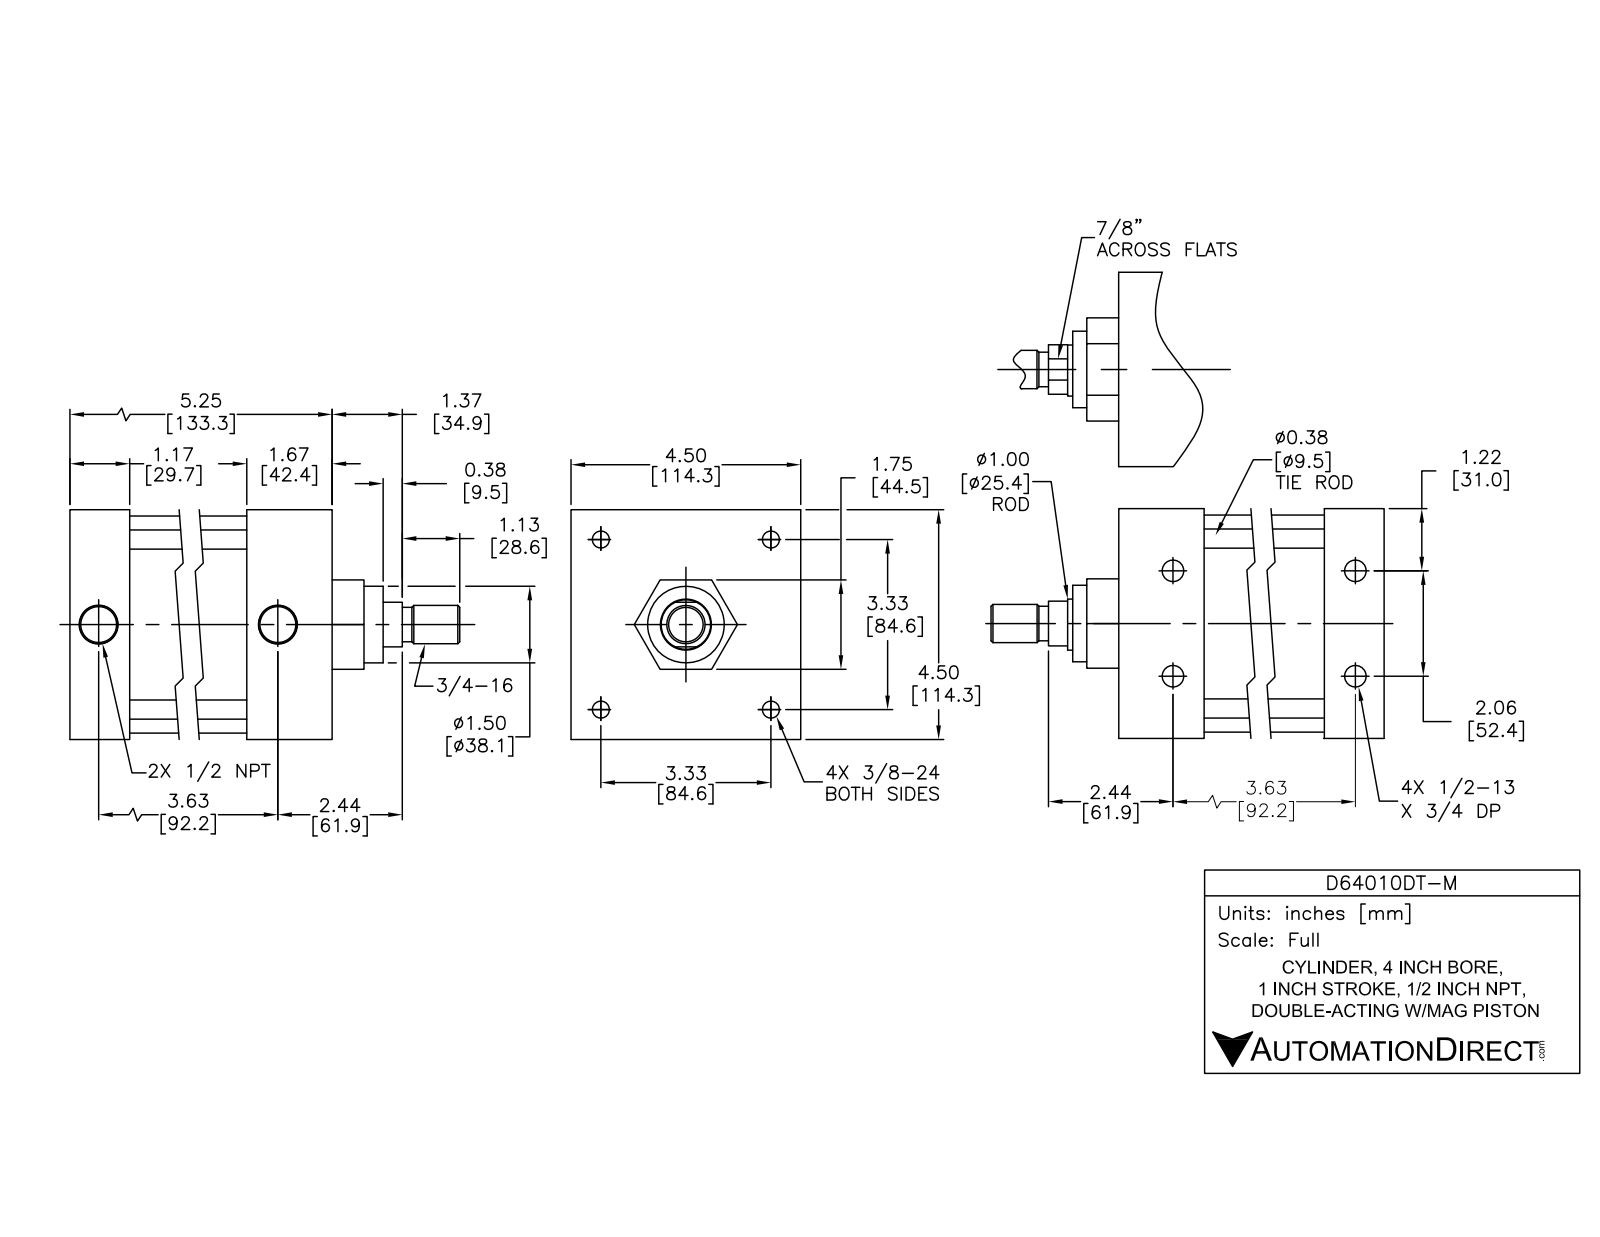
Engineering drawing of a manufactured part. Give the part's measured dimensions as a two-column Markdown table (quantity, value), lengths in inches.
| quantity | value |
| --- | --- |
| part name | D64010DT-M PISTON; D64010DT-M; D64010DT-M BODY |
| STEP written by | SolidWorks 2015 (AUTOMOTIVE_DESIGN) |
| units | inches |
| bodies | 12 solids, 303 faces (99 planar, 114 cylindrical, 90 other) |
| overall size | 7.745 × 4.5 × 4.5 |
| volume | 80.11 in³ |
| surface area | 323.7 in² |
| round holes (diameter × count) | 0.33 × 4, 0.406 × 4, 0.417 × 4, 0.625 × 4, 0.5 × 2, 0.766 × 2, 1 × 1, 1.003 × 1, 4 × 1 |
| round bosses / shafts (diameter × count) | 0.609 × 4, 0.375 × 4, 0.34 × 4, 4.25 × 1, 3.997 × 1, 1.75 × 1, 0.997 × 1, 0.97 × 1 |
| partial cylindrical surfaces (radius × count) | 0.45 × 4 |
| main face-to-face distances | 4.5, 0.08, 2.326, 5.246, 1.75, 3.997, 1.249, 2.751, 1.246, 2.495 |
| hole center spacings | 1.031, 2.349, 3.322, 3.766, 3.622, 2.062, 4.168, 4.698 |
